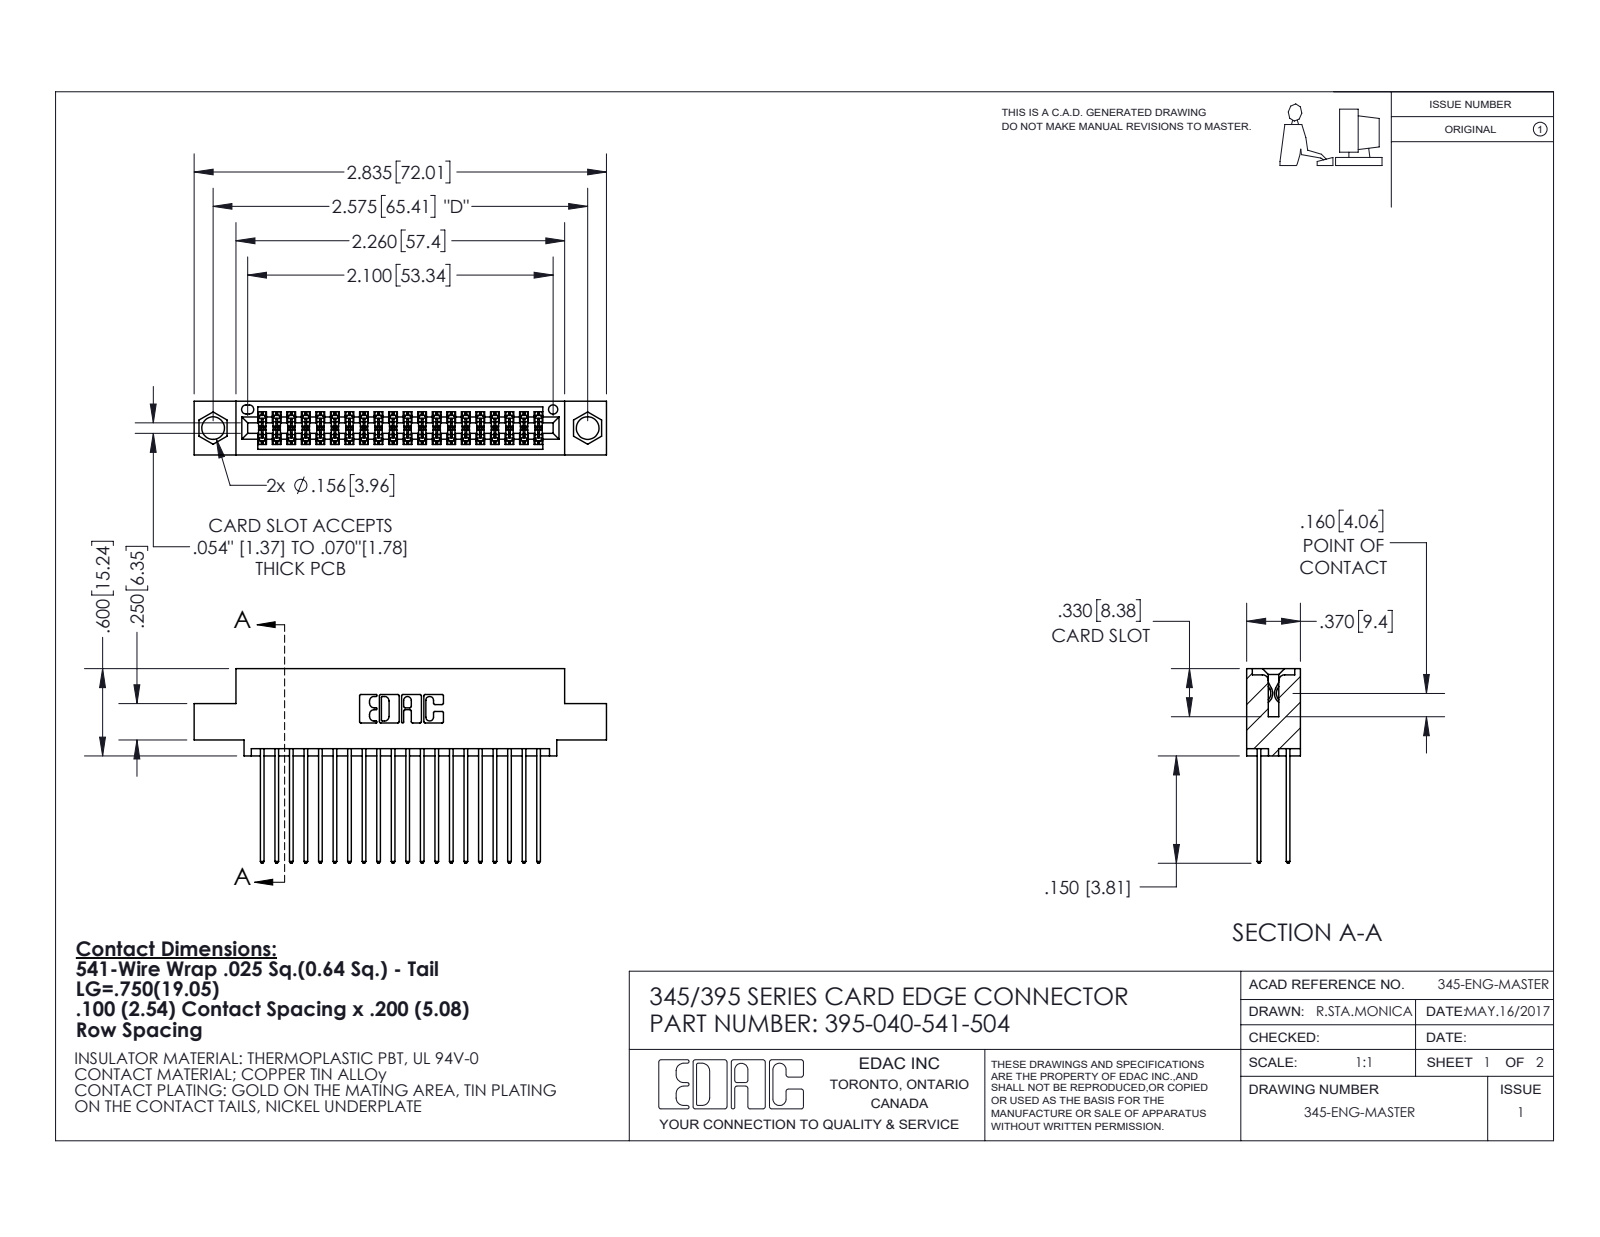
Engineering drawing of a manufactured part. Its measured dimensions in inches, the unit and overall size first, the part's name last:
Units: inches
Overall size (bounding box): 2.835 × 1.337 × 0.37
Round holes (diameter × count): ⌀0.156 ×2, ⌀0.064 ×1
Partial cylindrical surfaces — rounded edges, fillets, slot ends (radius × count): R0.006 ×60, R0.01 ×40, R0.01 ×22, R0.007 ×6, R0.031 ×6, R0.026 ×3, R0.014 ×2, R0.019 ×2
Main face-to-face distances: 0.072, 0.298, 0.2, 0.098, 0.272, 0.025, 0.37, 0.225, 0.175, 0.149
Hole centre spacings: 0.27, 2.341, 2.575
Volume: 0.417 in³ · Surface area: 16.6 in²
Bodies: 41 solids, 2144 faces (1418 planar, 726 cylindrical, 0 other)
Part name (STEP PRODUCT): 345 Part_0.110 Offset - 0.156 Dia-TI; 345-292-001_345-293-141; 395-040-541-504
STEP written by: SolidWorks 2020 (CONFIG_CONTROL_DESIGN)
